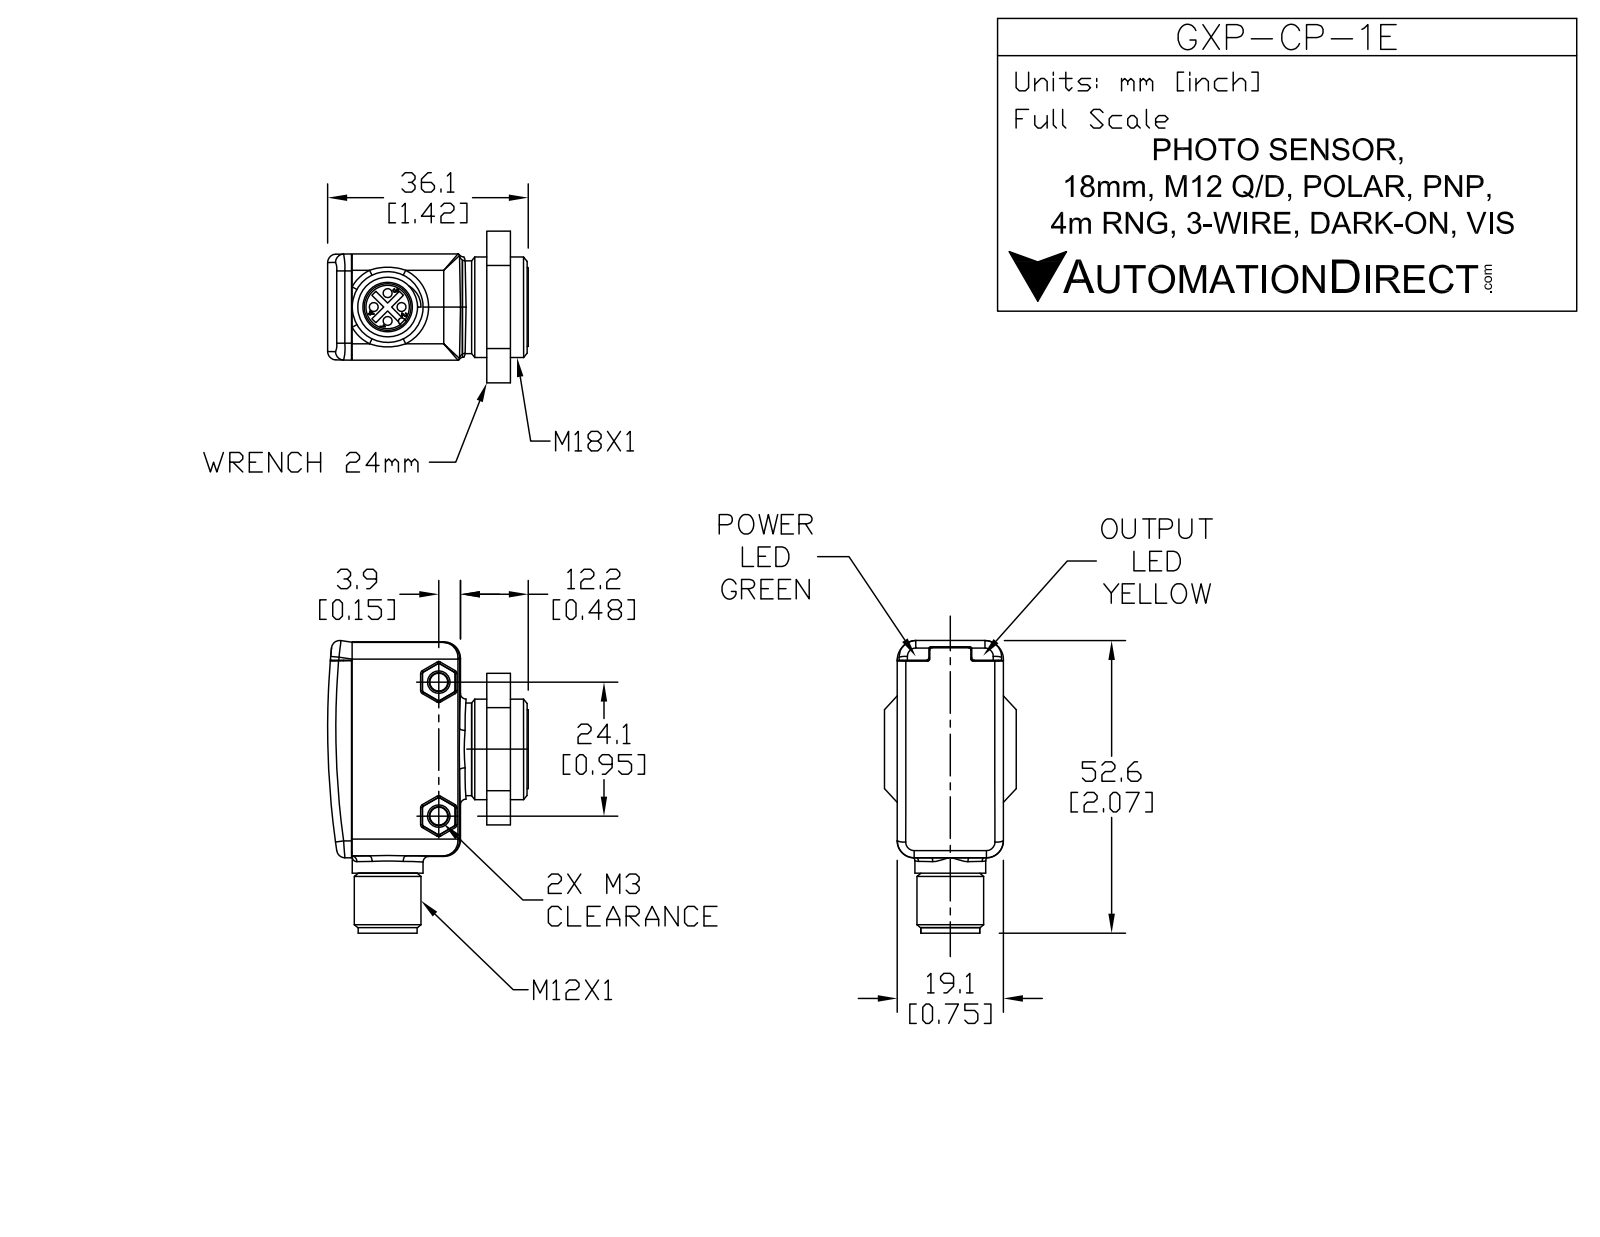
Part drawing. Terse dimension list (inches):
name: GXP-CP-1E
written by: SolidWorks 2013 (AUTOMOTIVE_DESIGN)
unit: in
bodies: 1 solid, 107 faces (60 planar, 33 cylindrical, 14 other)
size: 2.073 × 1.421 × 0.939
volume: 1.297 in³; area: 10 in²
holes: 2× ⌀0.126, 1× ⌀0.329
bosses: 1× ⌀0.709, 1× ⌀0.689, 1× ⌀0.559, 1× ⌀0.499, 1× ⌀0.455, 1× ⌀0.417
rounds: 8× R0.059, 4× R0.039, 1× R5.495
face distances: 0.752, 0.283, 0.083, 0.367, 0.756, 0.197, 0.113, 0.48, 1.528, 0.234
hole spacings: 0.949
